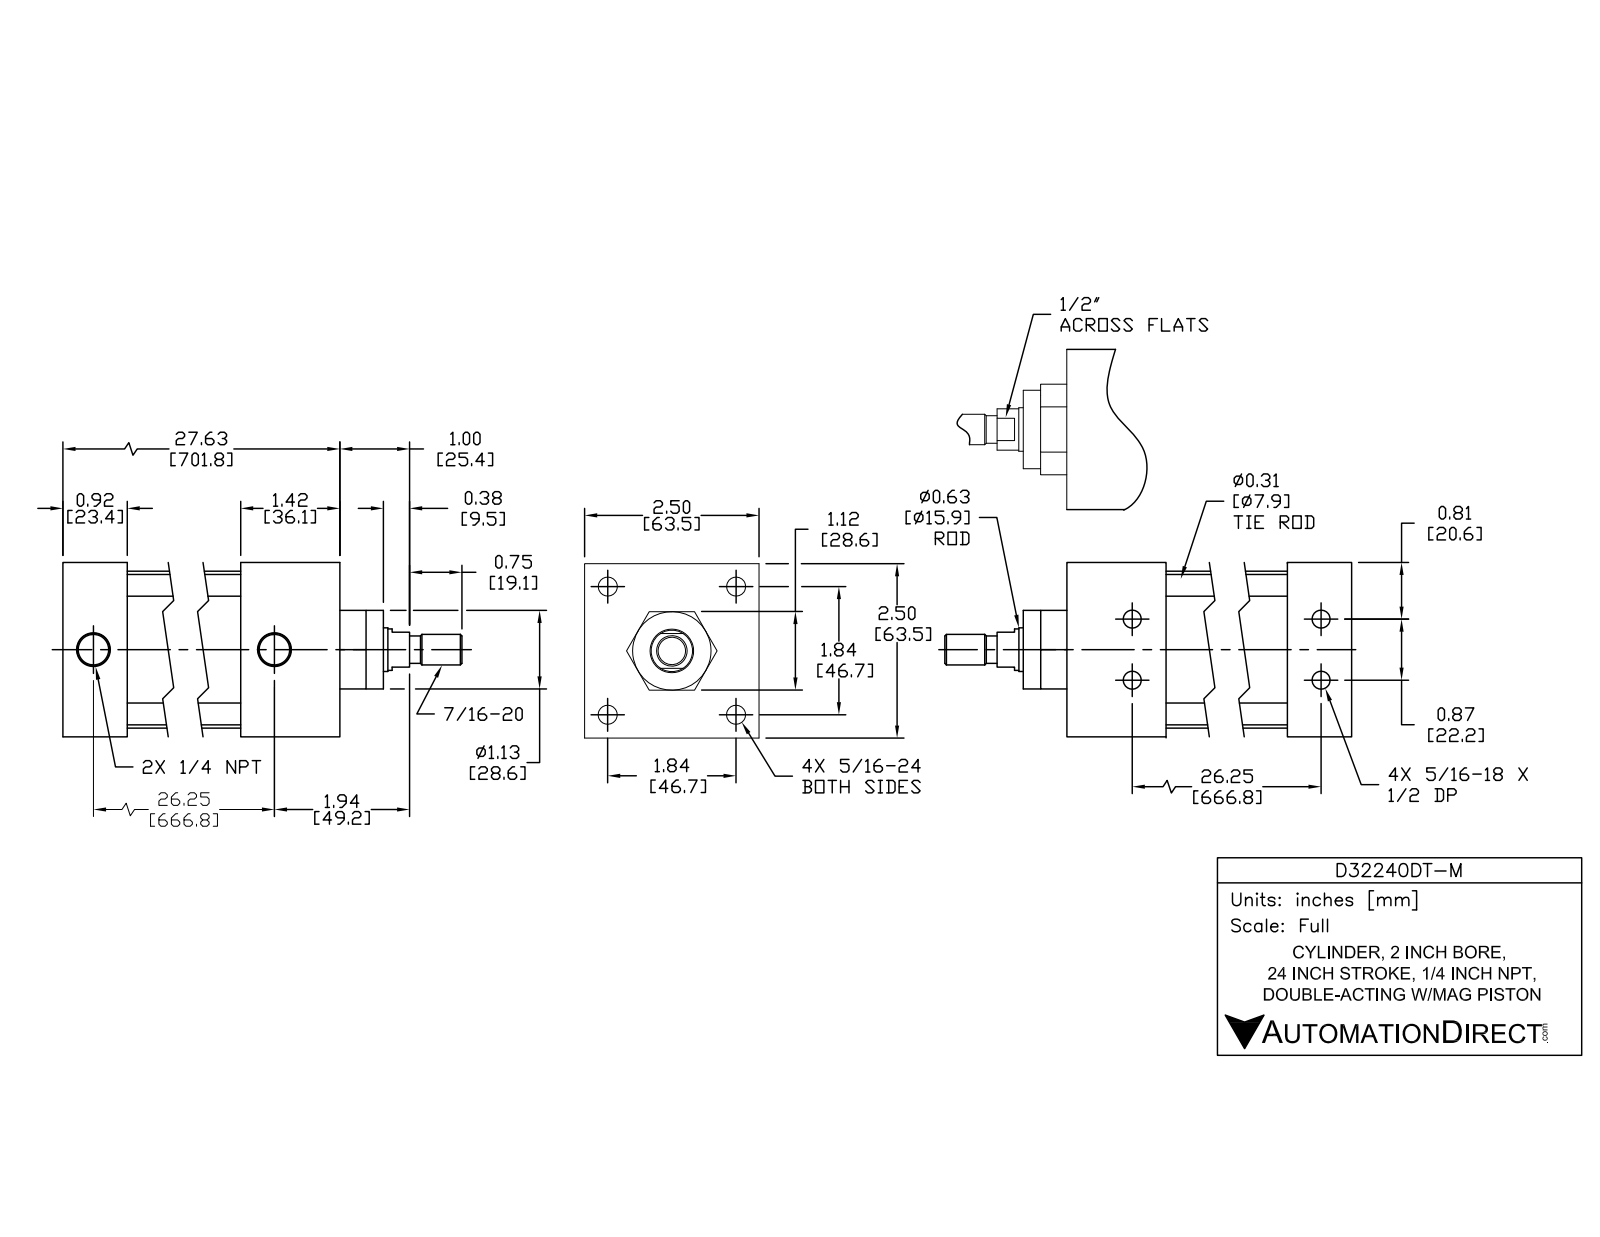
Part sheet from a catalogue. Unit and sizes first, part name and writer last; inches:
Units: inches
Overall size (bounding box): 29.371 × 2.5 × 2.5
Round holes (diameter × count): ⌀0.252 ×4, ⌀0.267 ×4, ⌀0.359 ×4, ⌀0.5 ×4, ⌀0.297 ×2, ⌀0.477 ×2, ⌀0.625 ×1, ⌀0.628 ×1, ⌀2 ×1
Round bosses / shafts (diameter × count): ⌀0.484 ×4, ⌀0.313 ×4, ⌀0.282 ×4, ⌀2.25 ×1, ⌀1.997 ×1, ⌀1.12 ×1, ⌀0.622 ×1, ⌀0.59 ×1
Partial cylindrical surfaces — rounded edges, fillets, slot ends (radius × count): R0.25 ×4
Main face-to-face distances: 2.5, 0.08, 25.201, 27.621, 1.42, 26.201, 26.701, 25.281, 0.92, 1
Hole centre spacings: 0.437, 1.307, 1.848, 26.249, 26.245, 0.875, 2.613, 26.26
Volume: 53.15 in³ · Surface area: 575.9 in²
Bodies: 12 solids, 298 faces (94 planar, 114 cylindrical, 90 other)
Part name (STEP PRODUCT): D32240DT-M PISTON; D32240DT-M BODY; D32240DT-M
STEP written by: SolidWorks 2015 (AUTOMOTIVE_DESIGN)
